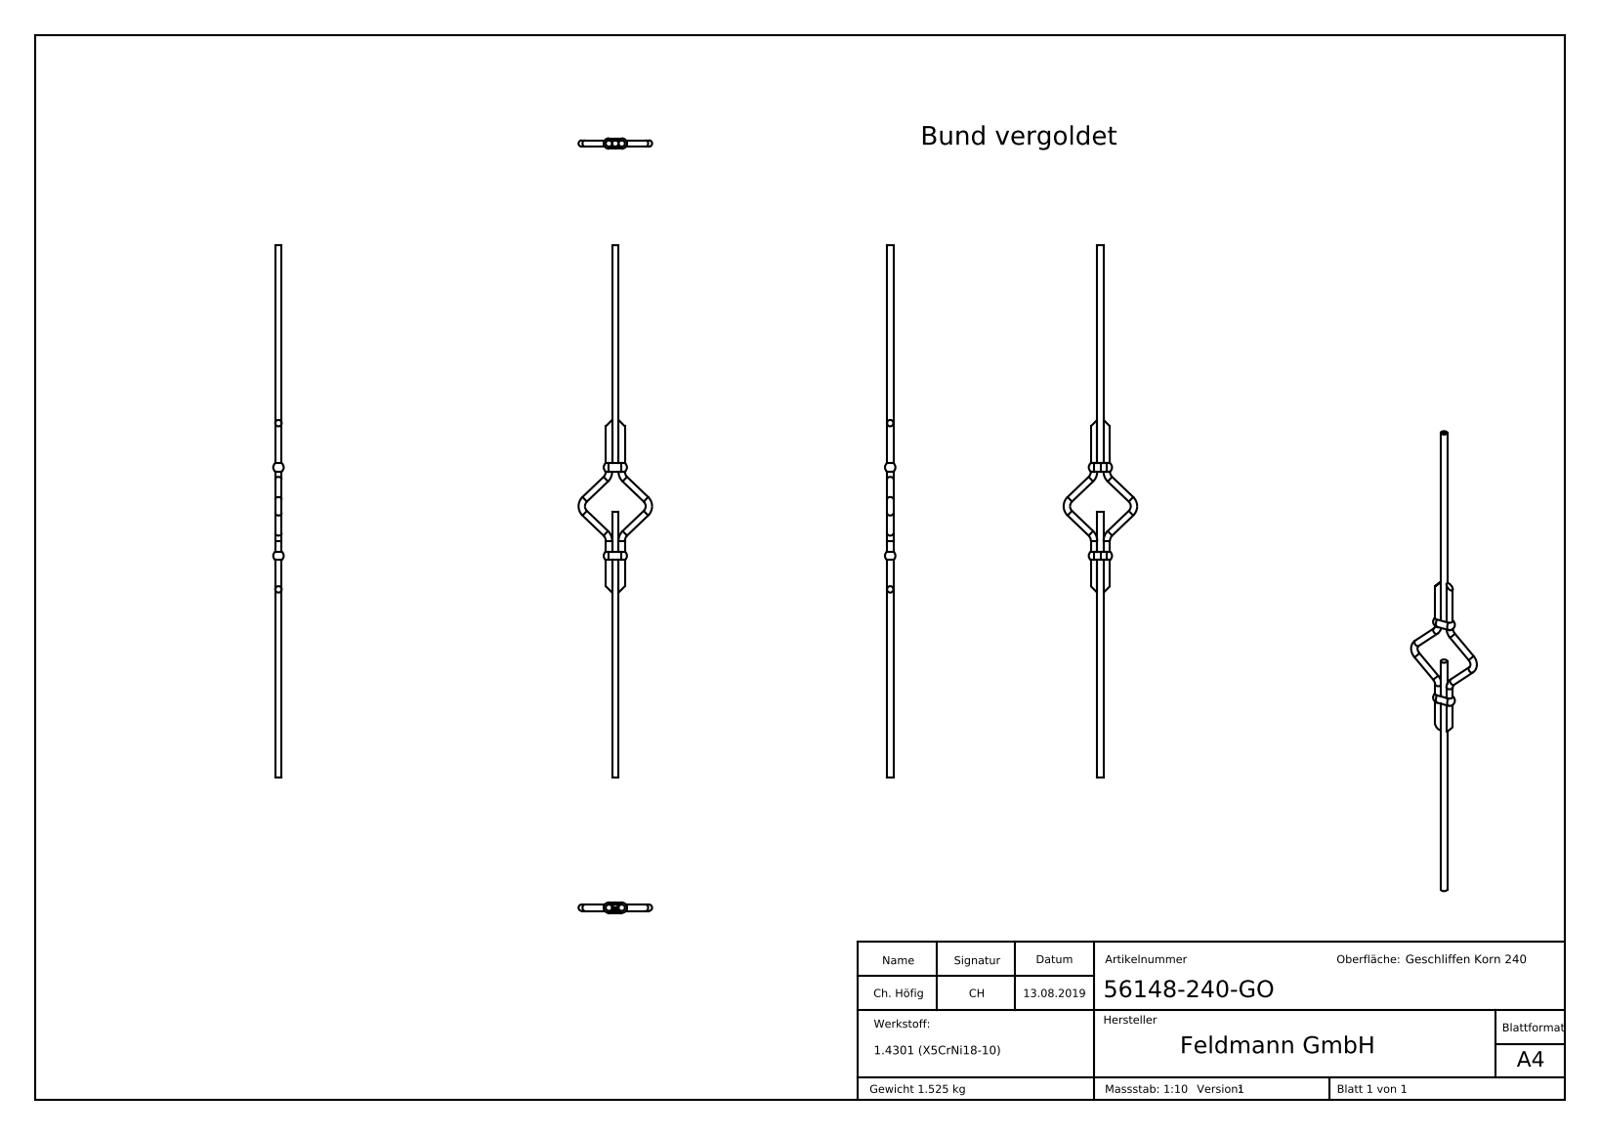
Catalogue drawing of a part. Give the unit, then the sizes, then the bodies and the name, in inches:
Units: inches
Overall size (bounding box): 39.37 × 5.433 × 0.772
Round bosses / shafts (diameter × count): ⌀0.472 ×7
Partial cylindrical surfaces — rounded edges, fillets, slot ends (radius × count): R0.406 ×4
Main face-to-face distances: 0.472, 9.353, 19.685, 22.638, 2.953, 39.37, 16.732, 39.366, 19.681, 16.728
Volume: 11.74 in³ · Surface area: 106.9 in²
Bodies: 6 solids, 323 faces (157 planar, 32 cylindrical, 134 other)
Part name (STEP PRODUCT): 56148-240-GO
STEP written by: SolidWorks 2015 (CONFIG_CONTROL_DESIGN)
